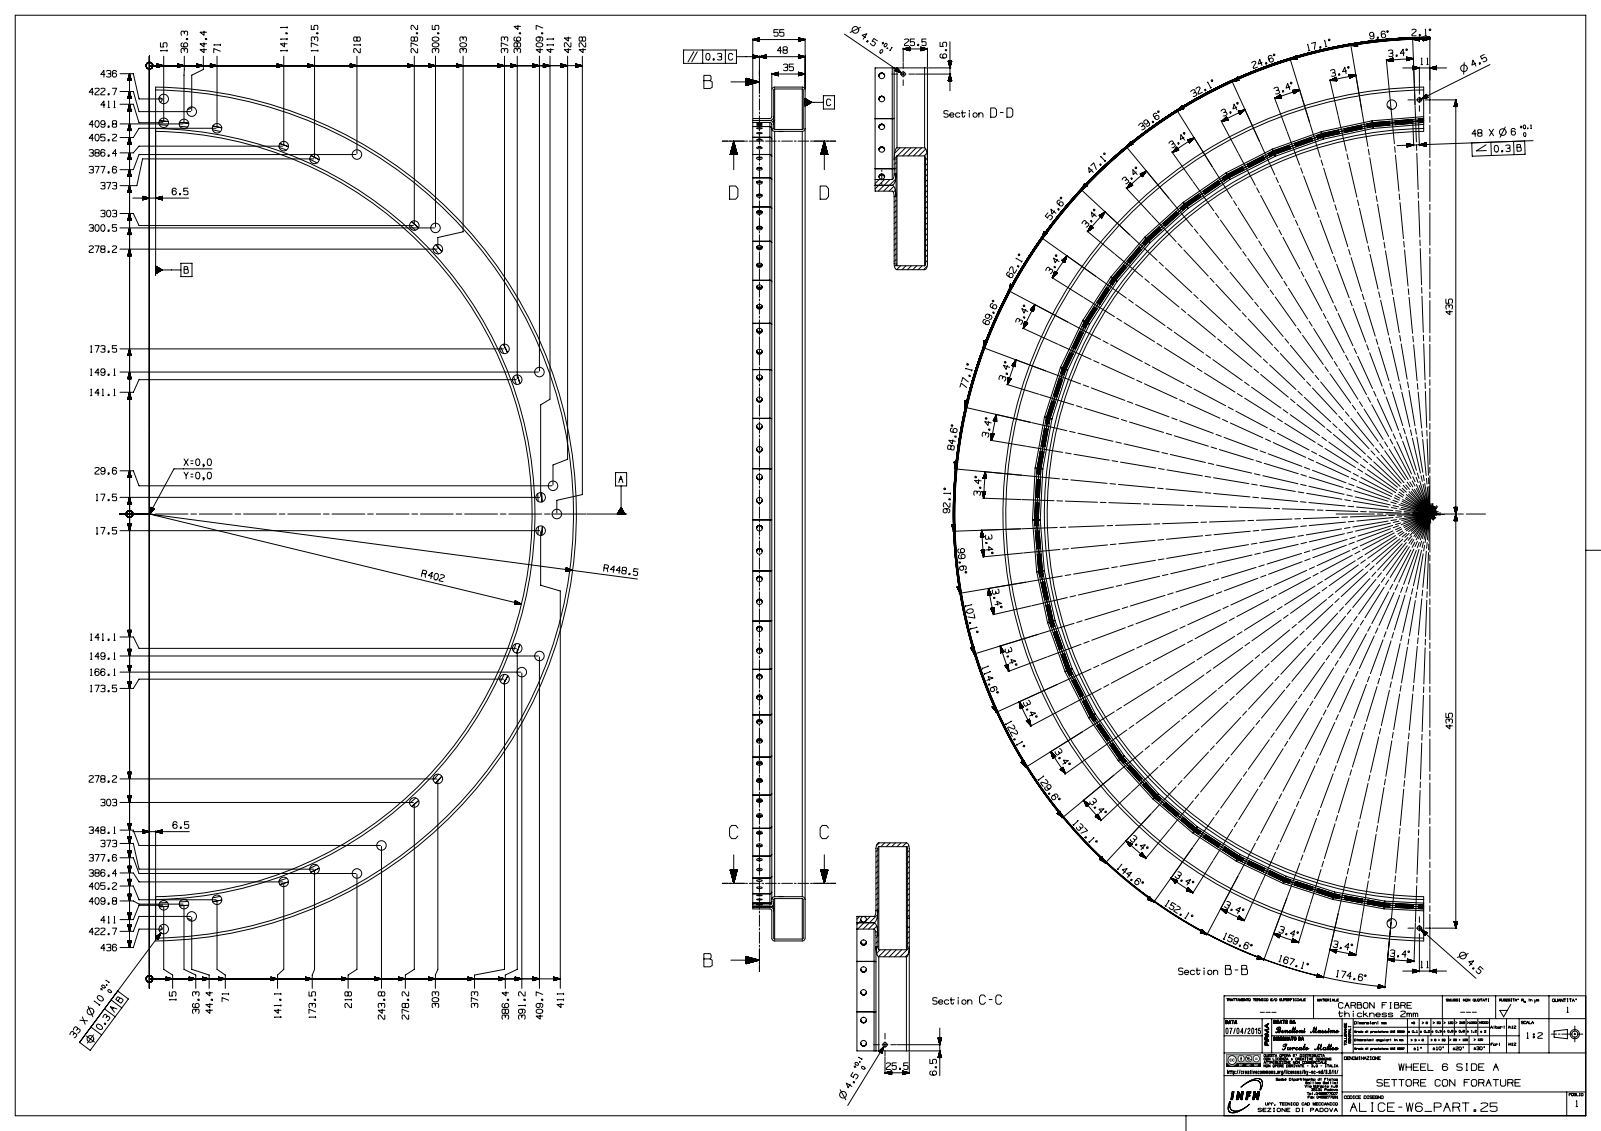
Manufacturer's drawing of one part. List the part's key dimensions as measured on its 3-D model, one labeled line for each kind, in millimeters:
Part name (STEP PRODUCT): turc17C413856and
STEP written by: SIEMENS PLM Software NX 8.5 (AP203_CONFIGURATION_CONTROLLED_3D_DESIGN_OF_MECHANICAL_PARTS_AND_ASSEMBLIES_MIM_LF)
Units: millimetres
Bodies: 1 solid, 533 faces (106 planar, 327 cylindrical, 100 other)
Overall size (bounding box): 896.91 × 442 × 55
Volume: 485 871 mm³ · Surface area: 497 723 mm²
Round holes (diameter × count): ⌀6 ×48, ⌀10 ×35, ⌀4.5 ×3
Partial cylindrical surfaces — rounded edges, fillets, slot ends (radius × count): R4 ×94, R2 ×71, R4.1 ×23, R402 ×1, R404 ×1, R446.5 ×1, R448.5 ×1
Main face-to-face distances: 2, 33, 31, 35, 2.1, 4.1, 55, 53, 22, 20
Hole centre spacings: 160.51, 35, 457.09, 126.04, 194.7, 264.46, 282.23, 314.85
